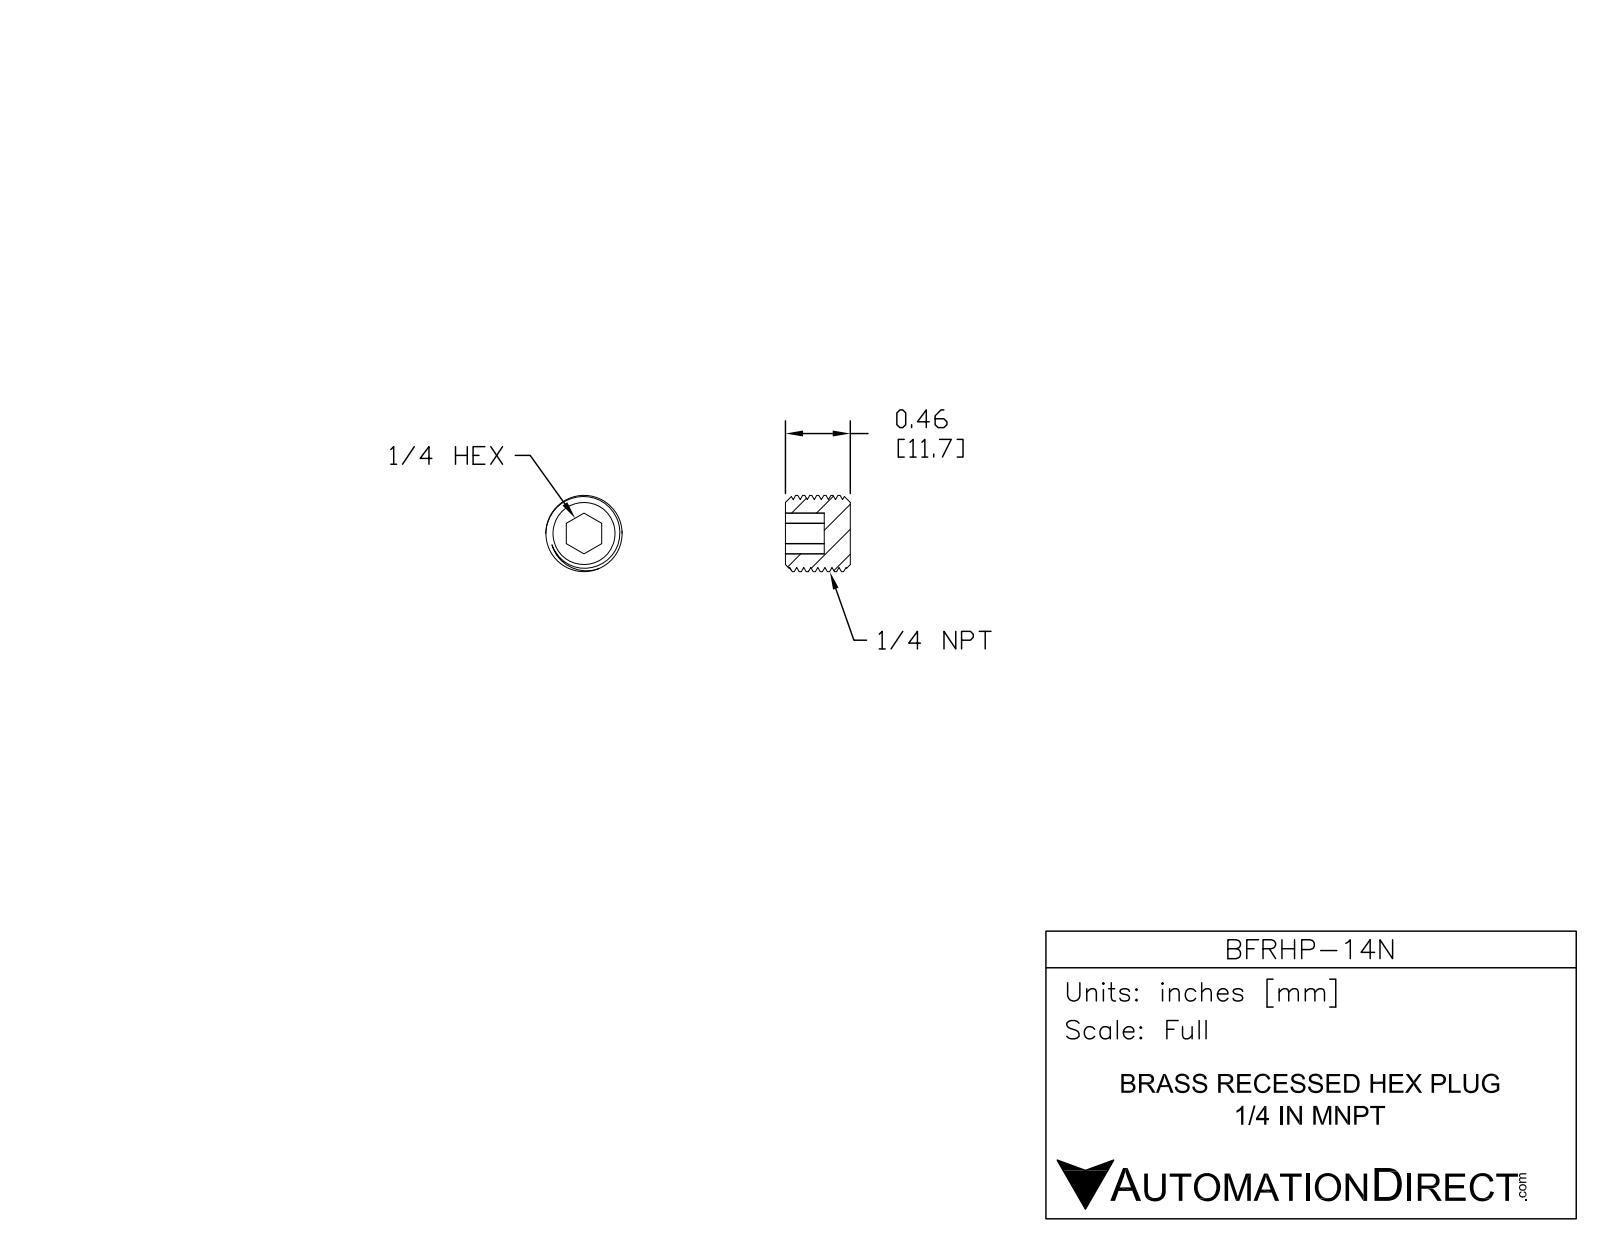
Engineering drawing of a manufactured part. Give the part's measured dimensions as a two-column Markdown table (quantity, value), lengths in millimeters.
| quantity | value |
| --- | --- |
| part name | BFRHP-14 |
| STEP written by | SolidWorks 2015 (CONFIG_CONTROL_DESIGN) |
| units | millimeters |
| bodies | 1 solid, 31 faces (9 planar, 16 cylindrical, 6 other) |
| overall size | 13.7 × 13.7 × 11.7 |
| volume | 1 300 mm³ |
| surface area | 1 128 mm² |
| round bosses / shafts (diameter × count) | 13.7 × 1 |
| main face-to-face distances | 11.7, 4.7, 7 |
